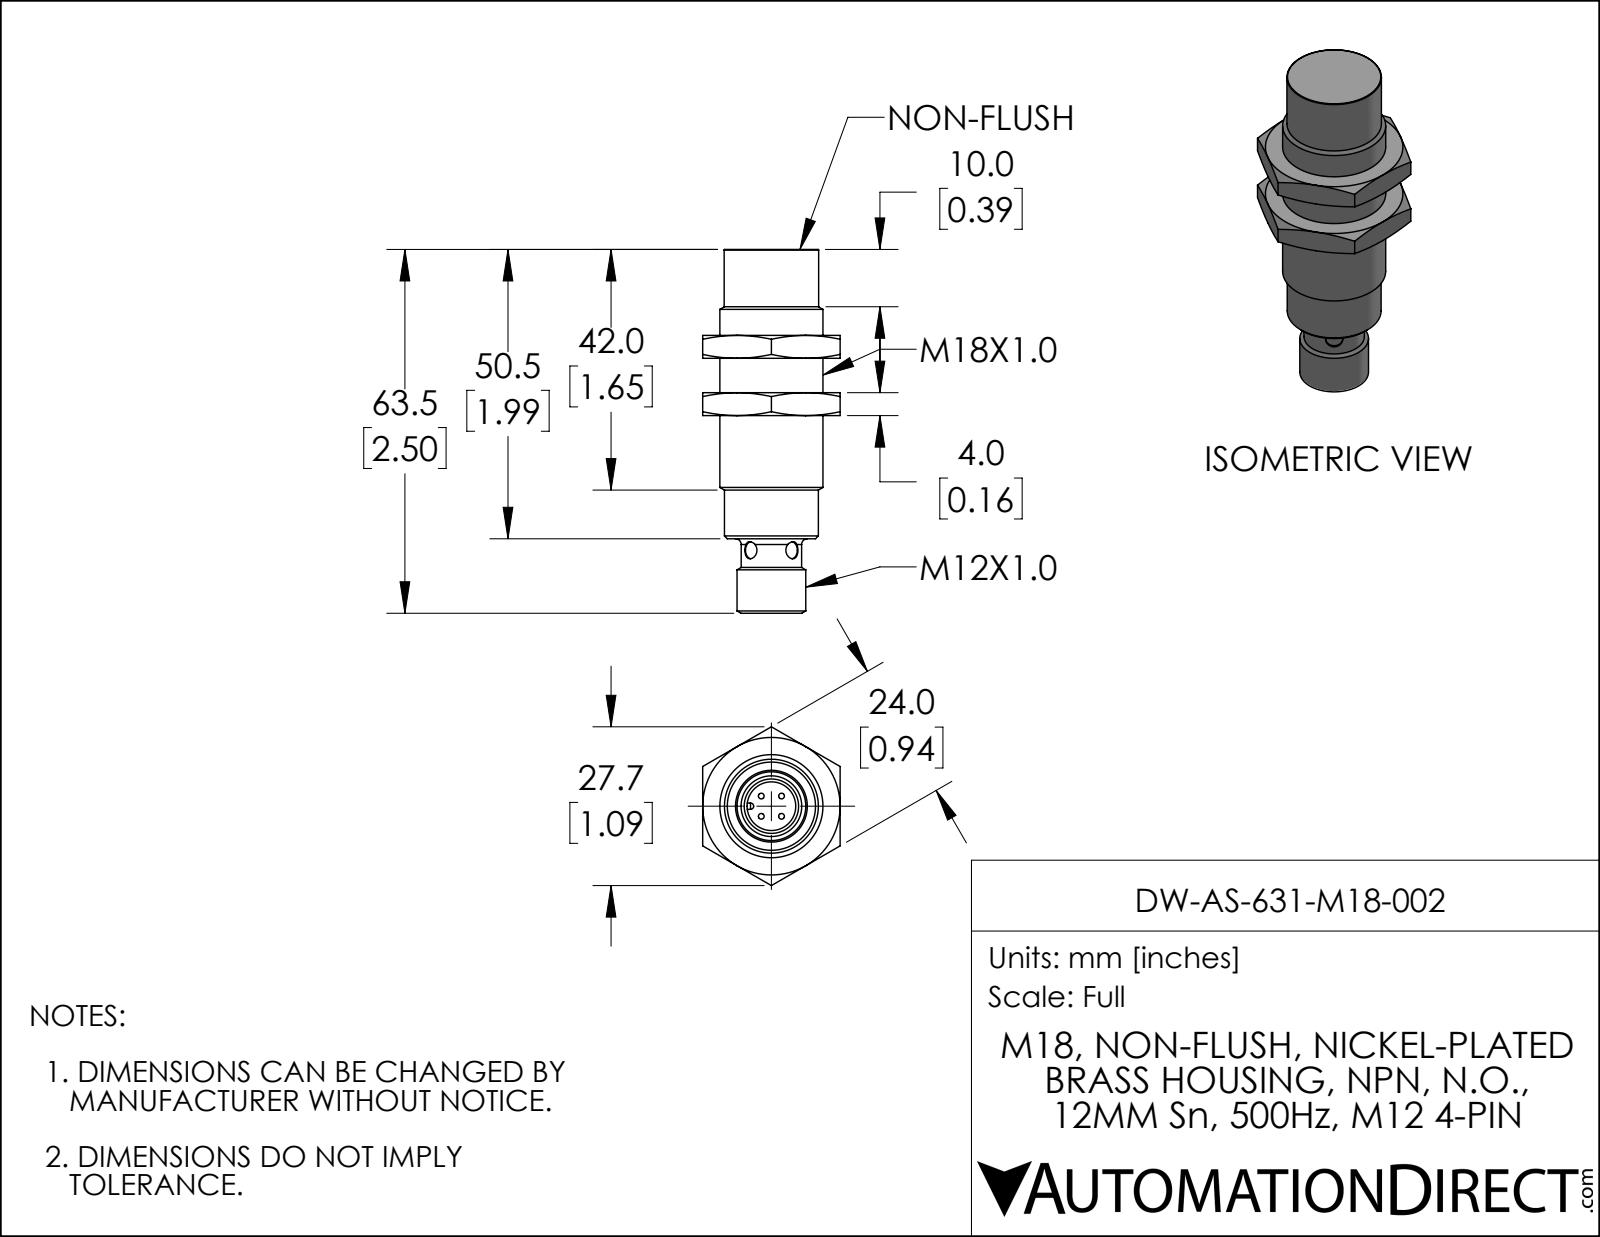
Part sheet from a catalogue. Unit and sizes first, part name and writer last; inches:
Units: inches
Overall size (bounding box): 2.5 × 1.091 × 0.945
Round holes (diameter × count): ⌀0.118 ×2, ⌀0.335 ×1
Round bosses / shafts (diameter × count): ⌀0.039 ×4, ⌀0.709 ×1, ⌀0.65 ×1, ⌀0.646 ×1, ⌀0.472 ×1, ⌀0.415 ×1
Partial cylindrical surfaces — rounded edges, fillets, slot ends (radius × count): R0.022 ×2
Main face-to-face distances: 0.394, 0.157, 0.945, 0.591, 0.748, 0.984, 1.142, 0.551, 0.236, 1.988
Volume: 0.905 in³ · Surface area: 8.001 in²
Bodies: 1 solid, 82 faces (27 planar, 18 cylindrical, 37 other)
Part name (STEP PRODUCT): DW-AS-631-M18-002
STEP written by: SolidWorks 2019 (AUTOMOTIVE_DESIGN)
